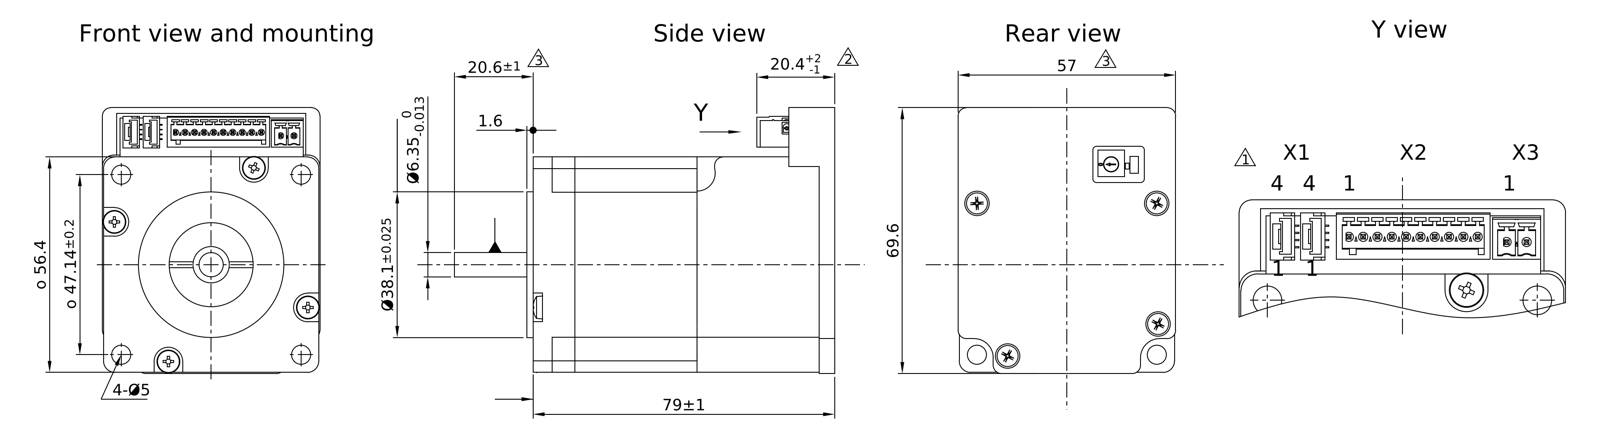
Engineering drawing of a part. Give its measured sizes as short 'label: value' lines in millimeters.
name: PD4-C5918M4204-E-08
written by: Autodesk Inventor 2013 (AUTOMOTIVE_DESIGN)
unit: mm
bodies: 0 solids, 1572 faces (1196 planar, 274 cylindrical, 102 other)
size: 99.6 × 69.6 × 57
holes: 8× ⌀2.5, 8× ⌀3, 6× ⌀2, 4× ⌀3.4, 4× ⌀5, 2× ⌀1.3, 2× ⌀1.5, 2× ⌀2.1, 1× ⌀3.78, 1× ⌀16.5, 1× ⌀22, 1× ⌀26
bosses: 12× ⌀1.2, 10× ⌀1.6, 4× ⌀5.5, 4× ⌀2.75, 4× ⌀2.68, 3× ⌀12, 2× ⌀0.46, 1× ⌀38.1
rounds: 26× R0.2, 20× R0.16, 18× R0.5, 16× R2.3, 12× R3, 10× R1, 10× R2.2, 8× R0.21
face distances: 56.4, 36, 5, 31, 10.8, 2.4, 5.8, 12, 25.2, 8.4
hole spacings: 34.82, 39.19, 43.22, 47.14, 4.4, 12.5, 14.15, 19.32
